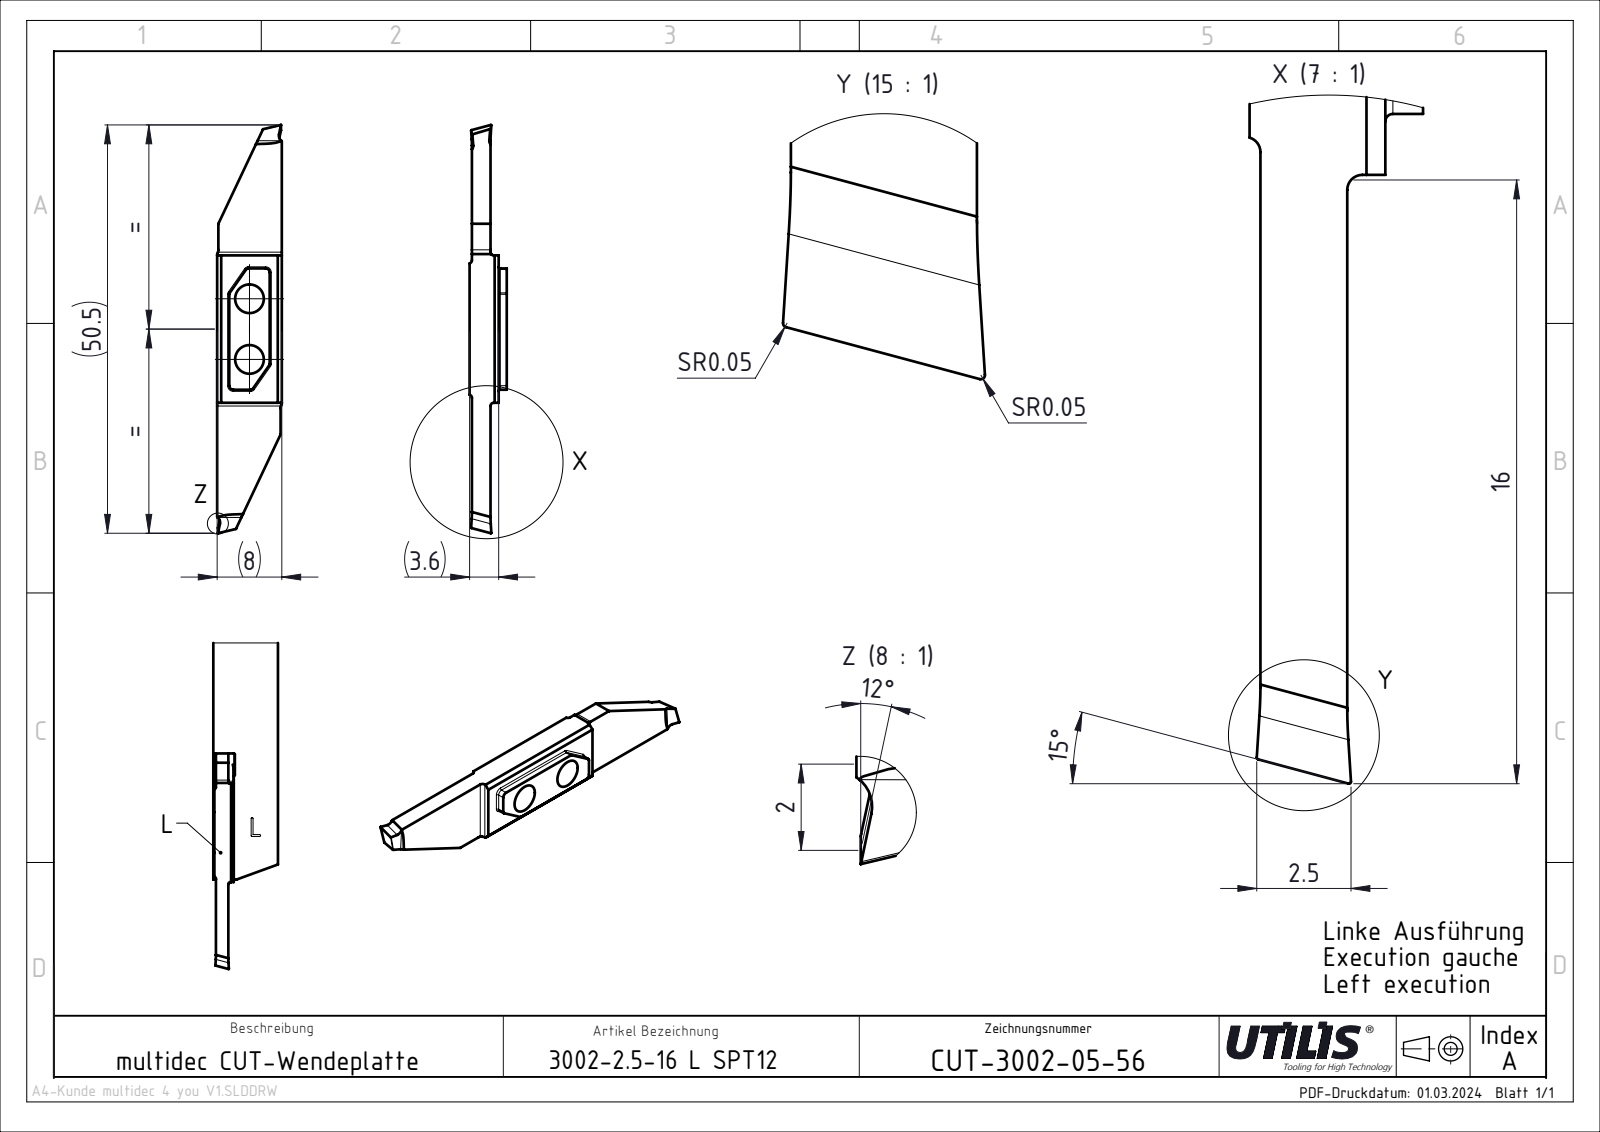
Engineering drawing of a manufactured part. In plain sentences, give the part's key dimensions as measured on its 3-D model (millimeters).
The part is named "CUT-3002 SPT Slim_and_Deep; ASME Y14.5". Its 3-D file was written by "SolidWorks 2023 SP4 || FormatWorks Professional (AP242_MANAGED_MODEL_BASED_3D_ENGINEERING_MIM_LF)". It is 1 solid with 36 faces: 22 planar, 14 cylindrical and 0 other. Overall it measures 50.5 by 8 by 3.6 millimeters. Its volume is 864 cubic millimeters and its surface area 993 square millimeters. Round holes: 2 of diameter 3.55. Partial cylindrical surfaces (rounded edges, fillets, slot ends): 4 of radius 0.4, 2 of radius 1. The main face-to-face distances are 2.3, 2.59, 3.6, 3.31, 1.01, 8, 18.09, 7.85, 7.7, 18.22. The hole center spacings are 7.5.
